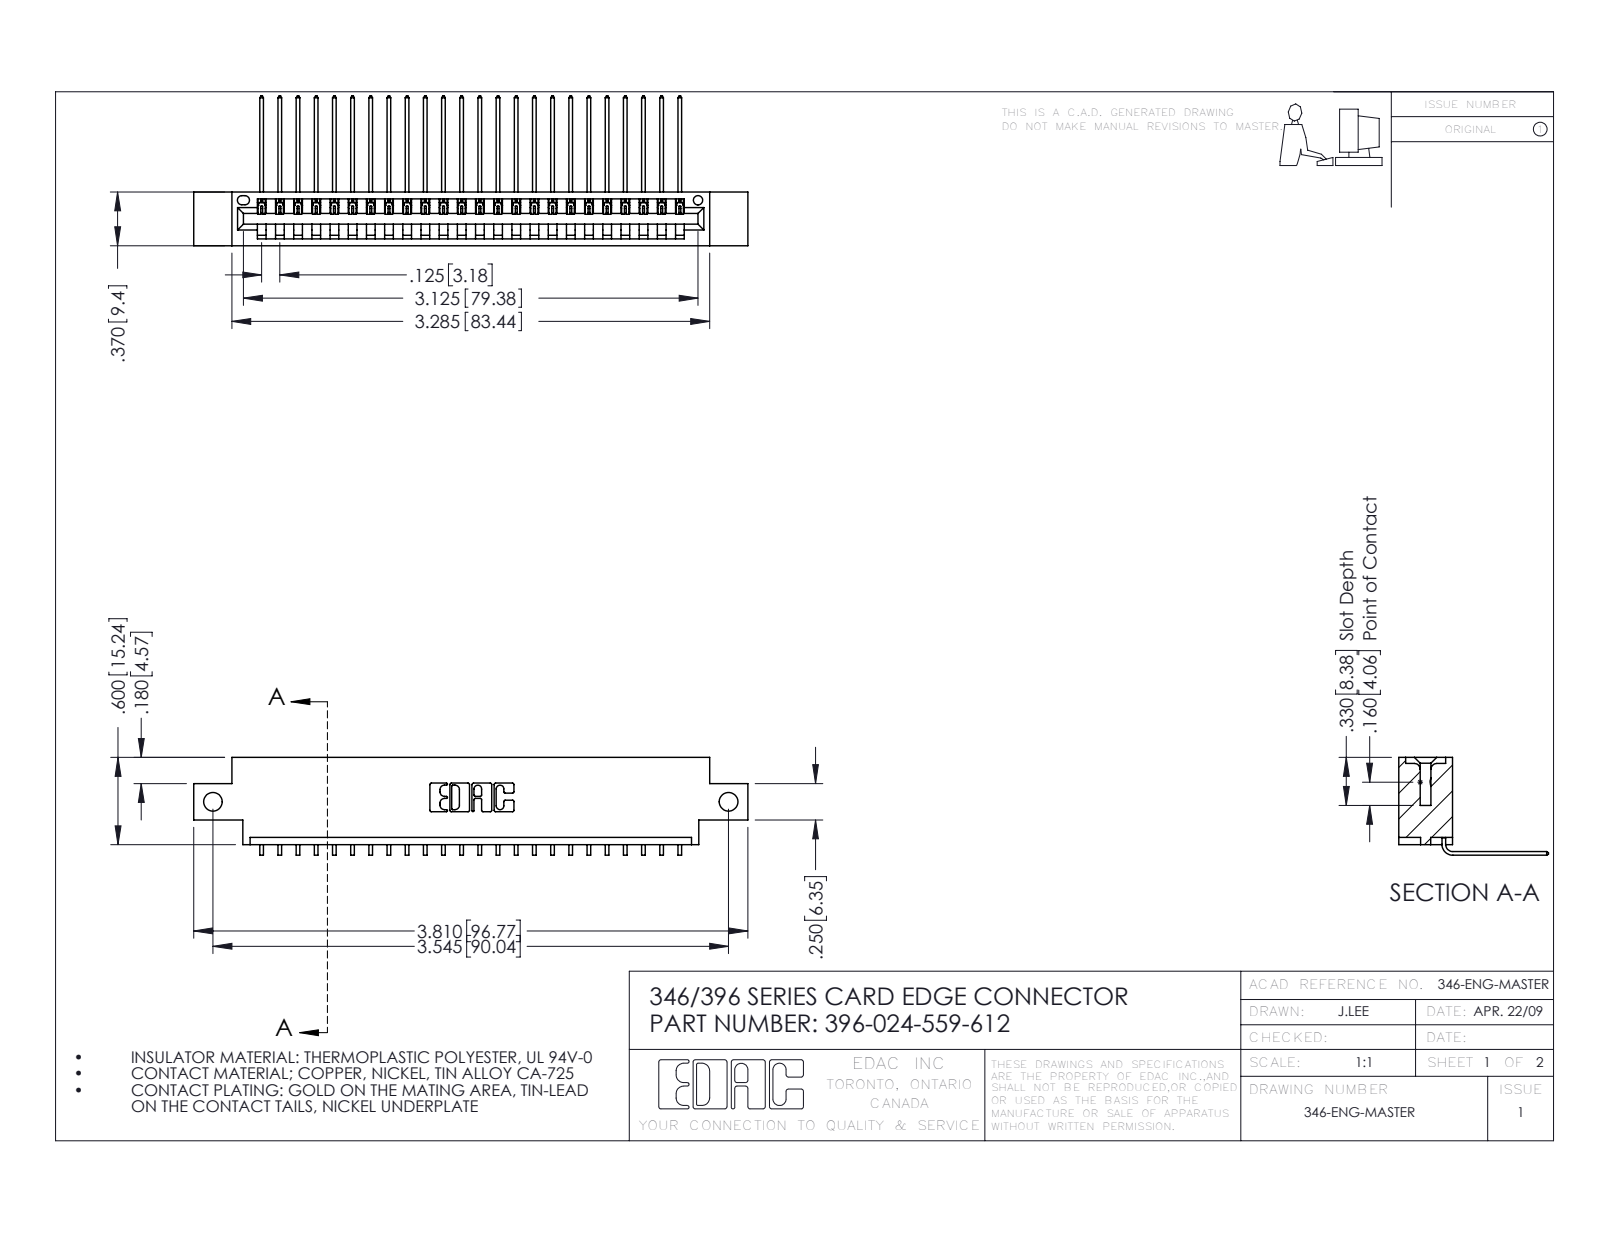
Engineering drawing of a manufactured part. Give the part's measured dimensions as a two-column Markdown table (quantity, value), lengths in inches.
| quantity | value |
| --- | --- |
| part name | 396-024-559-612; 345-292-001_558 559 Tail - 1; 346 Part_0.170 Offset - Side Mount |
| STEP written by | SolidWorks 2016 (CONFIG_CONTROL_DESIGN) |
| units | inches |
| bodies | 25 solids, 1566 faces (1088 planar, 478 cylindrical, 0 other) |
| overall size | 3.81 × 1.03 × 0.673 |
| volume | 0.548 in³ |
| surface area | 17.85 in² |
| round holes (diameter × count) | 0.128 × 2, 0.064 × 1 |
| partial cylindrical surfaces (radius × count) | 0.006 × 48, 0.01 × 22, 0.007 × 6, 0.031 × 6, 0.026 × 3, 0.031 × 2, 0.04 × 2, 0.014 × 1 |
| main face-to-face distances | 0.048, 0.322, 0.37, 0.25, 0.025, 0.072, 0.148, 0.222, 0.1, 0.174 |
| hole center spacings | 3.545 |
